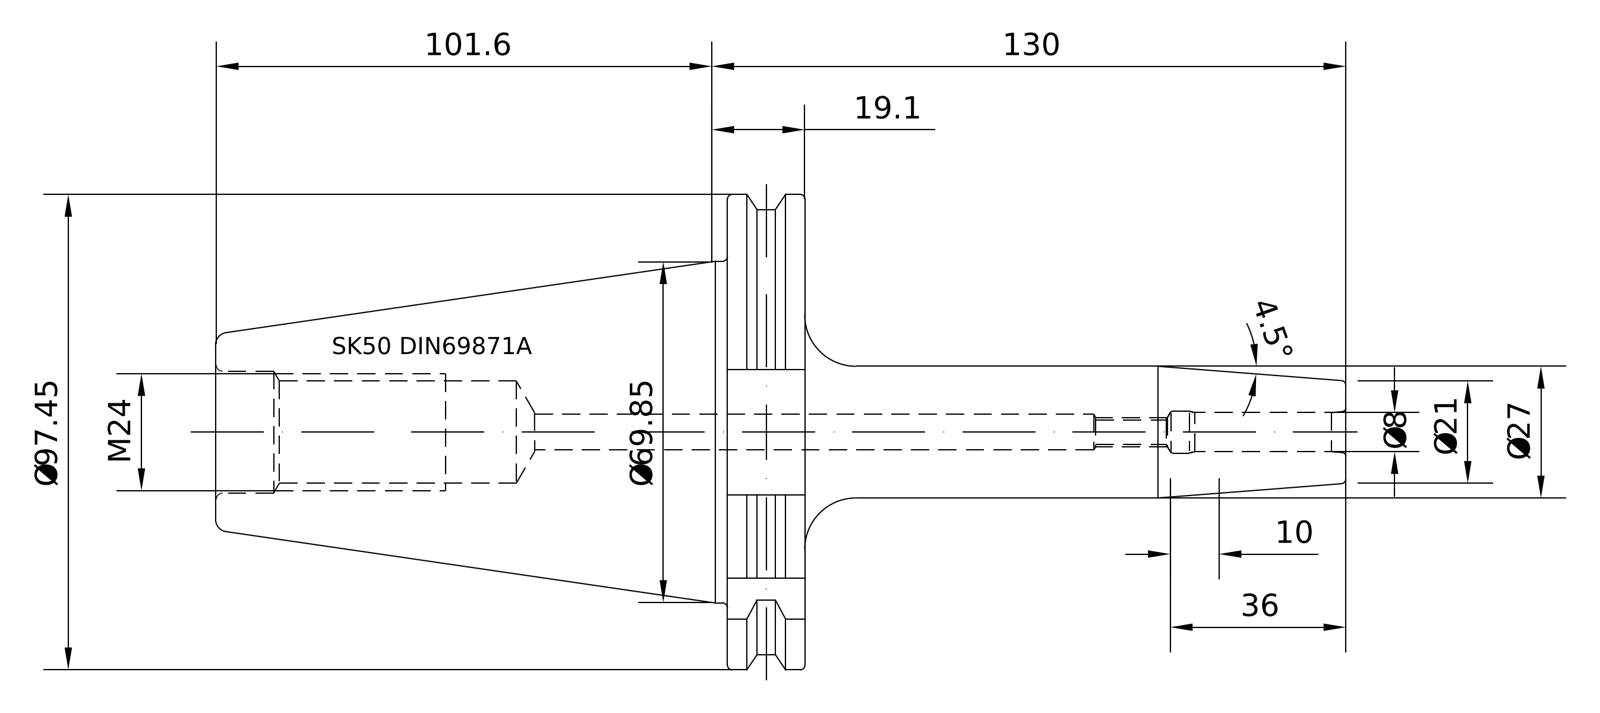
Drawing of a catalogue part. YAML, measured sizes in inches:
part_name: "50-444-08"
step_written_by: "PRO/ENGINEER BY PARAMETRIC TECHNOLOGY CORPORATION, 2010430 (CONFIG_CONTROL_DESIGN)"
units: inches
bodies: {solids: 1, faces: 93, planar: 21, cylindrical: 24, other: 48}
overall_size: [9.118, 3.837, 3.701]
volume: 24.39
surface_area: 80.58
round_holes:
  - {diameter: 0.315, count: 1}
  - {diameter: 0.817, count: 1}
  - {diameter: 0.985, count: 1}
  - {diameter: 1.012, count: 1}
round_bosses_or_shafts:
  - {diameter: 3.583, count: 1}
  - {diameter: 2.722, count: 1}
  - {diameter: 1.063, count: 1}
  - {diameter: 0.945, count: 1}
partial_cylinders:
  - {radius: 0.069, count: 1}
  - {radius: 1.919, count: 1}
face_to_face_distances: [0.624, 2.866, 4.126, 4.75, 1.016, 9.118, 4.992, 4.368, 1.89, 2.236]
